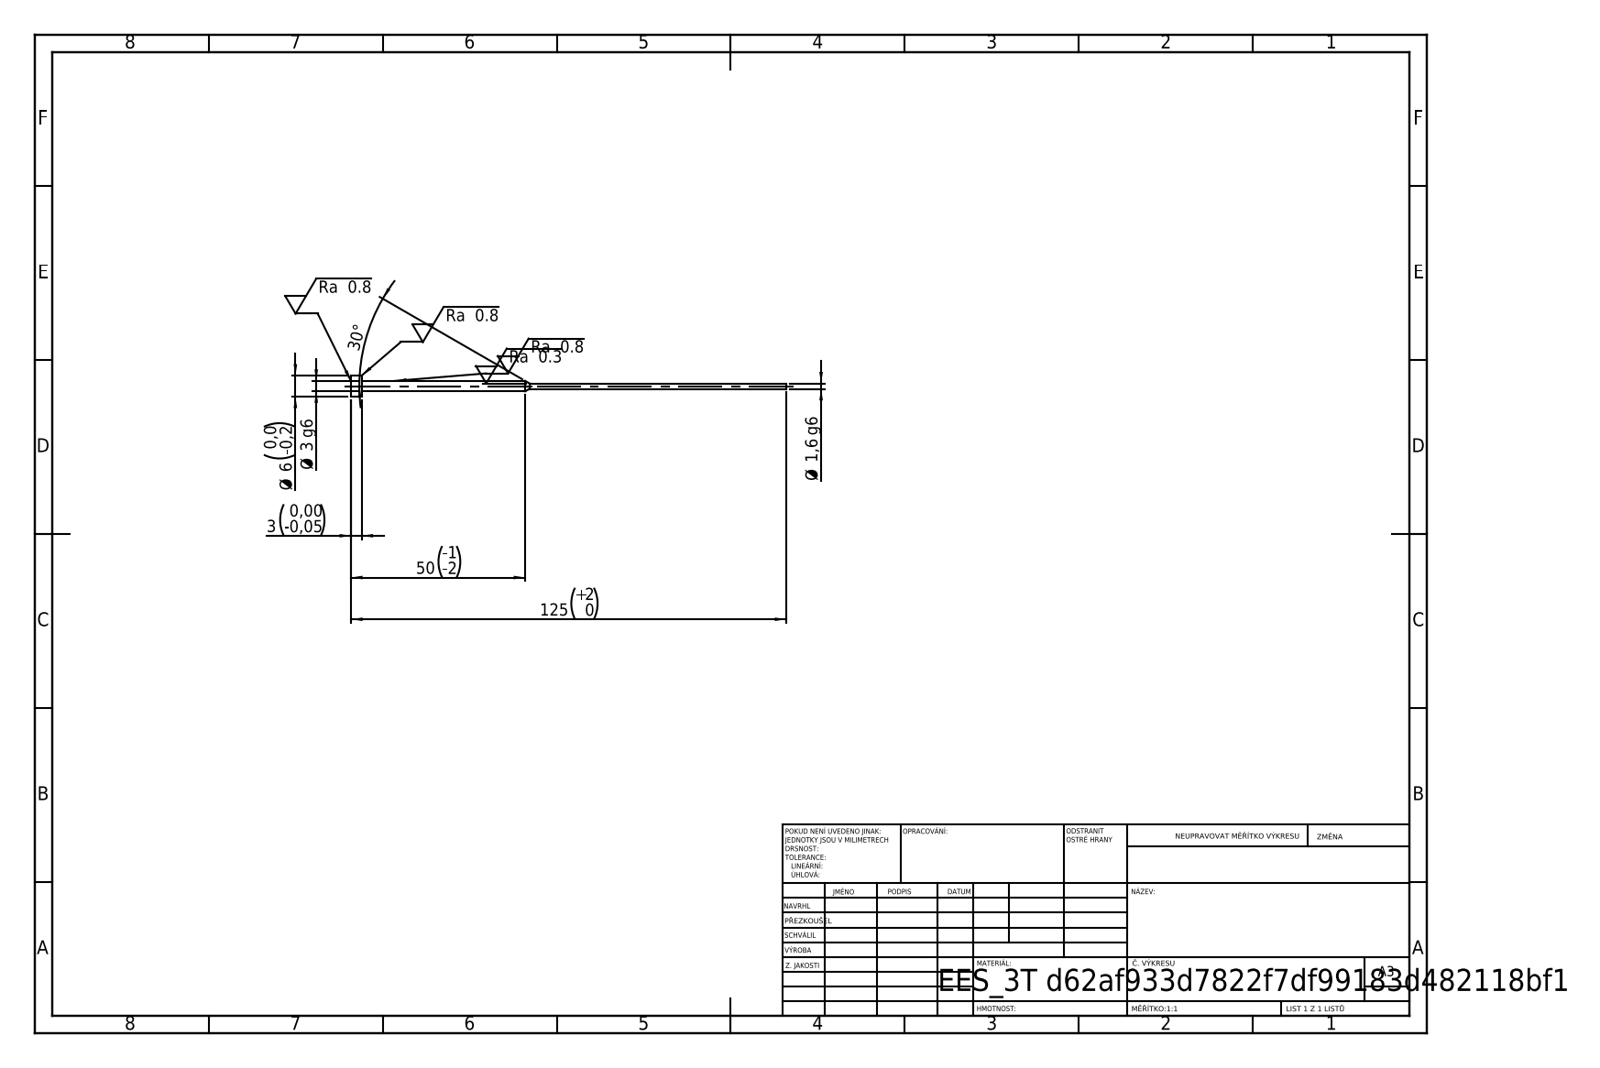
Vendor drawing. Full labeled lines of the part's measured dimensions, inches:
STEP written by: SolidWorks 2019 (CONFIG_CONTROL_DESIGN)
Units: inches
Bodies: 1 solid, 11 faces (3 planar, 6 cylindrical, 2 other)
Overall size (bounding box): 4.921 × 0.236 × 0.236
Volume: 0.035 in³ · Surface area: 1.44 in²
Round bosses / shafts (diameter × count): ⌀0.236 ×1, ⌀0.118 ×1, ⌀0.063 ×1
Main face-to-face distances: 0.118, 4.803, 4.921
